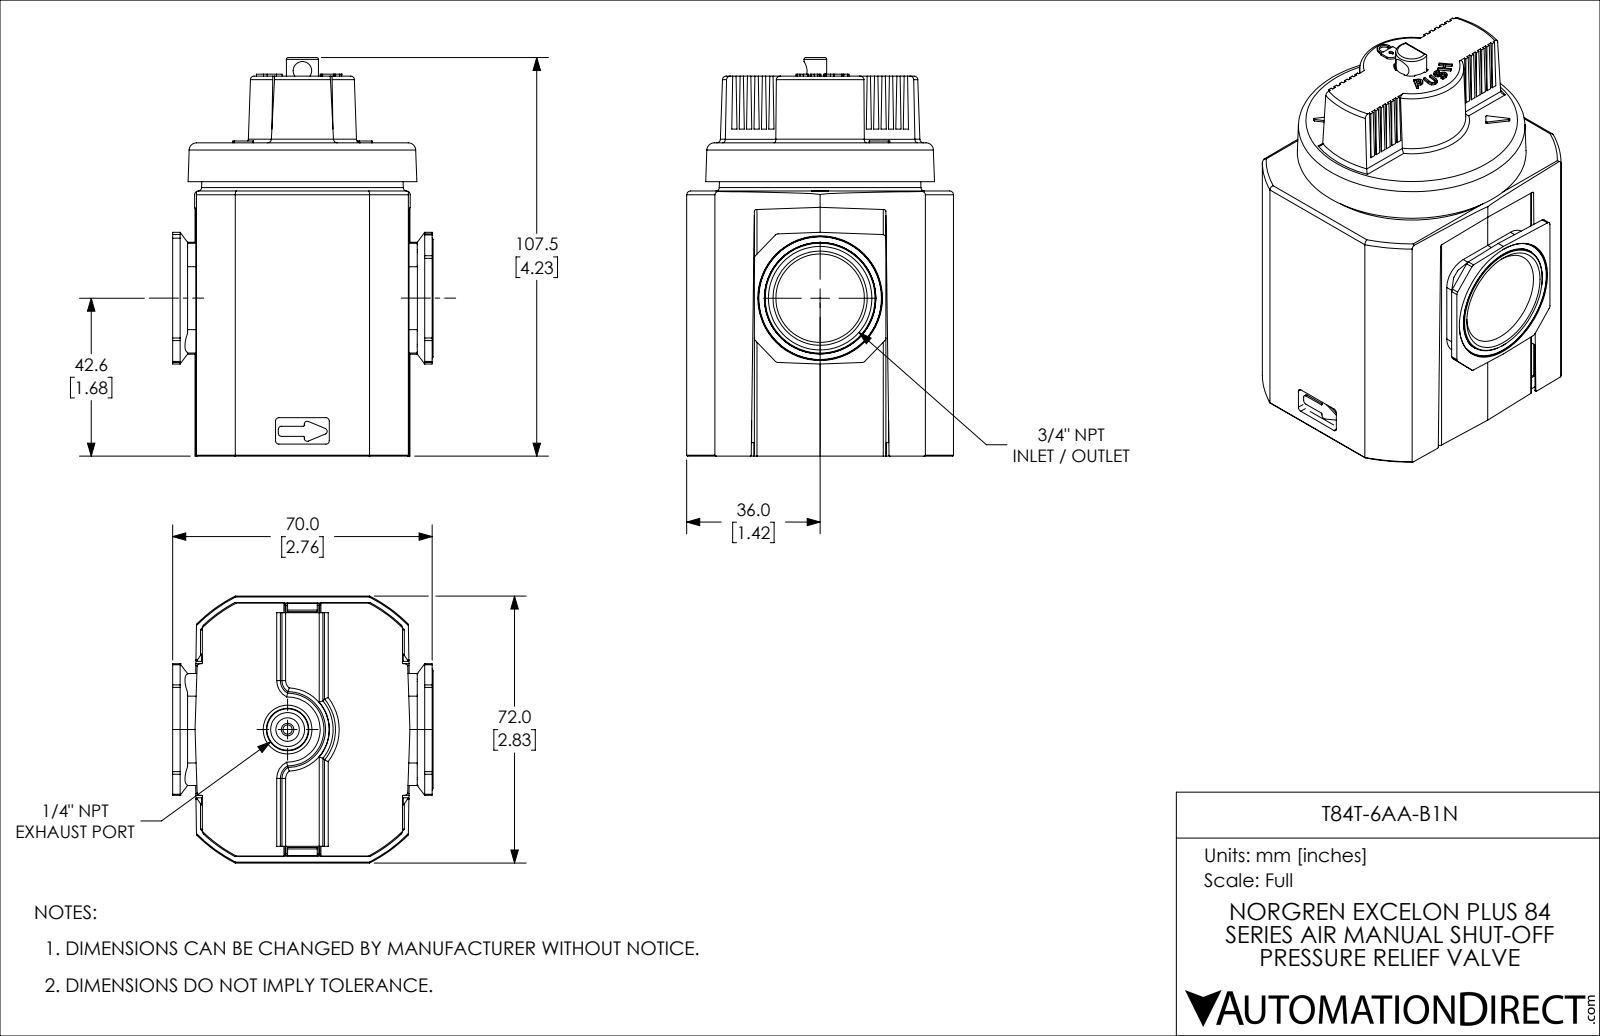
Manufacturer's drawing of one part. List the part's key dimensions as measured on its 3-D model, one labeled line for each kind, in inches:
Part name (STEP PRODUCT): T84T-6AA-B1N
STEP written by: SolidWorks 2021 (CONFIG_CONTROL_DESIGN)
Units: inches
Bodies: 3 solids, 712 faces (365 planar, 227 cylindrical, 120 other)
Overall size (bounding box): 4.232 × 2.835 × 2.766
Volume: 11.56 in³ · Surface area: 124.8 in²
Round holes (diameter × count): ⌀0.039 ×1, ⌀0.197 ×1, ⌀0.451 ×1, ⌀1.551 ×1
Round bosses / shafts (diameter × count): ⌀0.984 ×1, ⌀0.669 ×1
Partial cylindrical surfaces — rounded edges, fillets, slot ends (radius × count): R0.039 ×30, R0.03 ×16, R0.01 ×15, R0.02 ×9, R0.035 ×4, R0.079 ×4, R0.157 ×4, R0.248 ×4
Main face-to-face distances: 2.913, 2.835, 2.756, 0.157, 0.413, 0.144, 2.77, 0.709, 2.281, 0.512
Hole centre spacings: 0.157, 0.315
